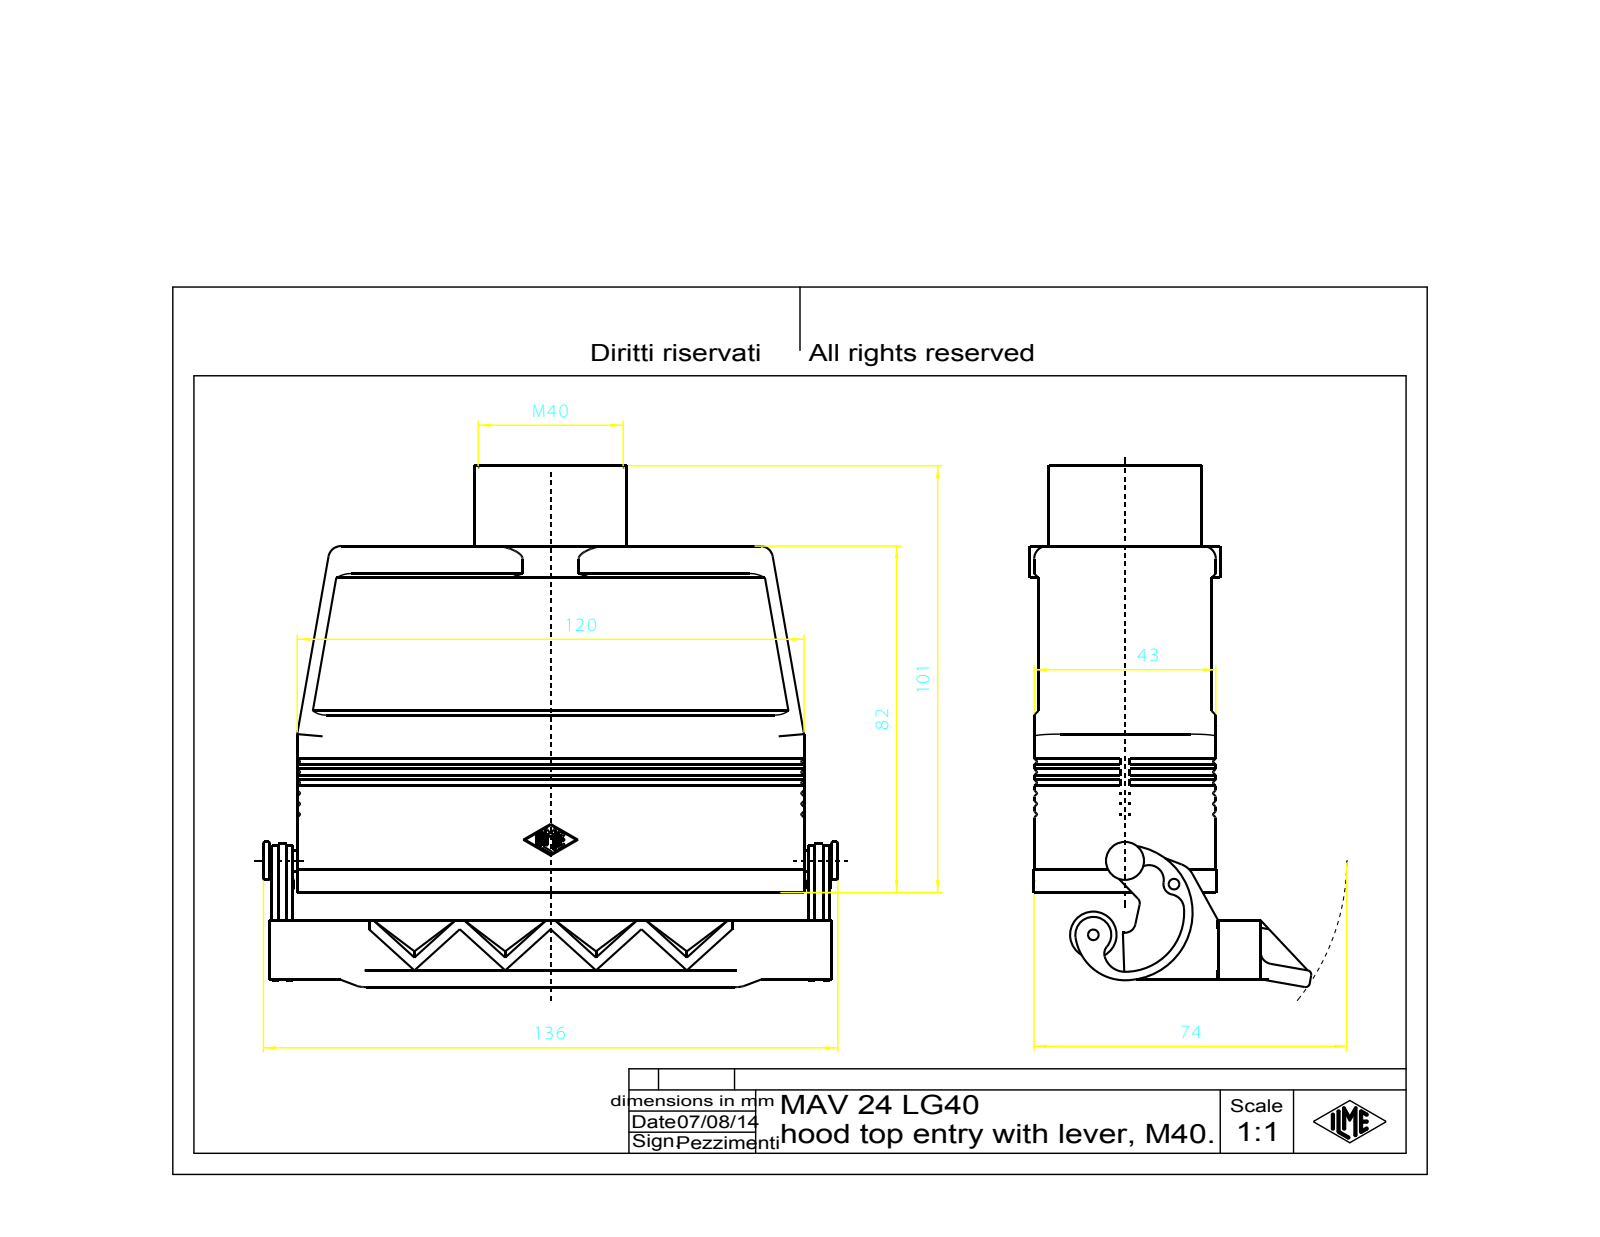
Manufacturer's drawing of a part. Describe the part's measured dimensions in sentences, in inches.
The part is named "MAV_24_LG40". Its 3-D file was written by "Creo Elements/Direct Modeling 18.0B 02-Dec-2011 (C) Parametric Technology GmbH (AUTOMOTIVE_DESIGN)". It is 1 solid with 806 faces: 358 planar, 257 cylindrical and 191 other. Overall it measures 5.354 by 4.857 by 2.641 inches. Its volume is 8.058 cubic inches and its surface area 117.9 square inches. Round holes: 4 of diameter 0.079, 4 of diameter 0.122, 1 of diameter 0.098, 1 of diameter 1.339, 1 of diameter 1.575. Round bosses or shafts: 1 of diameter 1.811, 1 of diameter 1.772, 1 of diameter 0.433, 1 of diameter 0.354, 1 of diameter 0.197, 1 of diameter 0.122, 1 of diameter 0.079. Partial cylindrical surfaces (rounded edges, fillets, slot ends): 38 of radius 0.01, 28 of radius 0.008, 9 of radius 0.098, 8 of radius 0.236, 7 of radius 0.118, 6 of radius 0.039, 5 of radius 0.059, 4 of radius 0.096. The main face-to-face distances are 0.138, 0.136, 1.557, 1.555, 0.098, 0.096, 0.039, 1.518, 1.654, 1.516. The hole center spacings are 2.115, 1.063, 4.094, 4.23.
